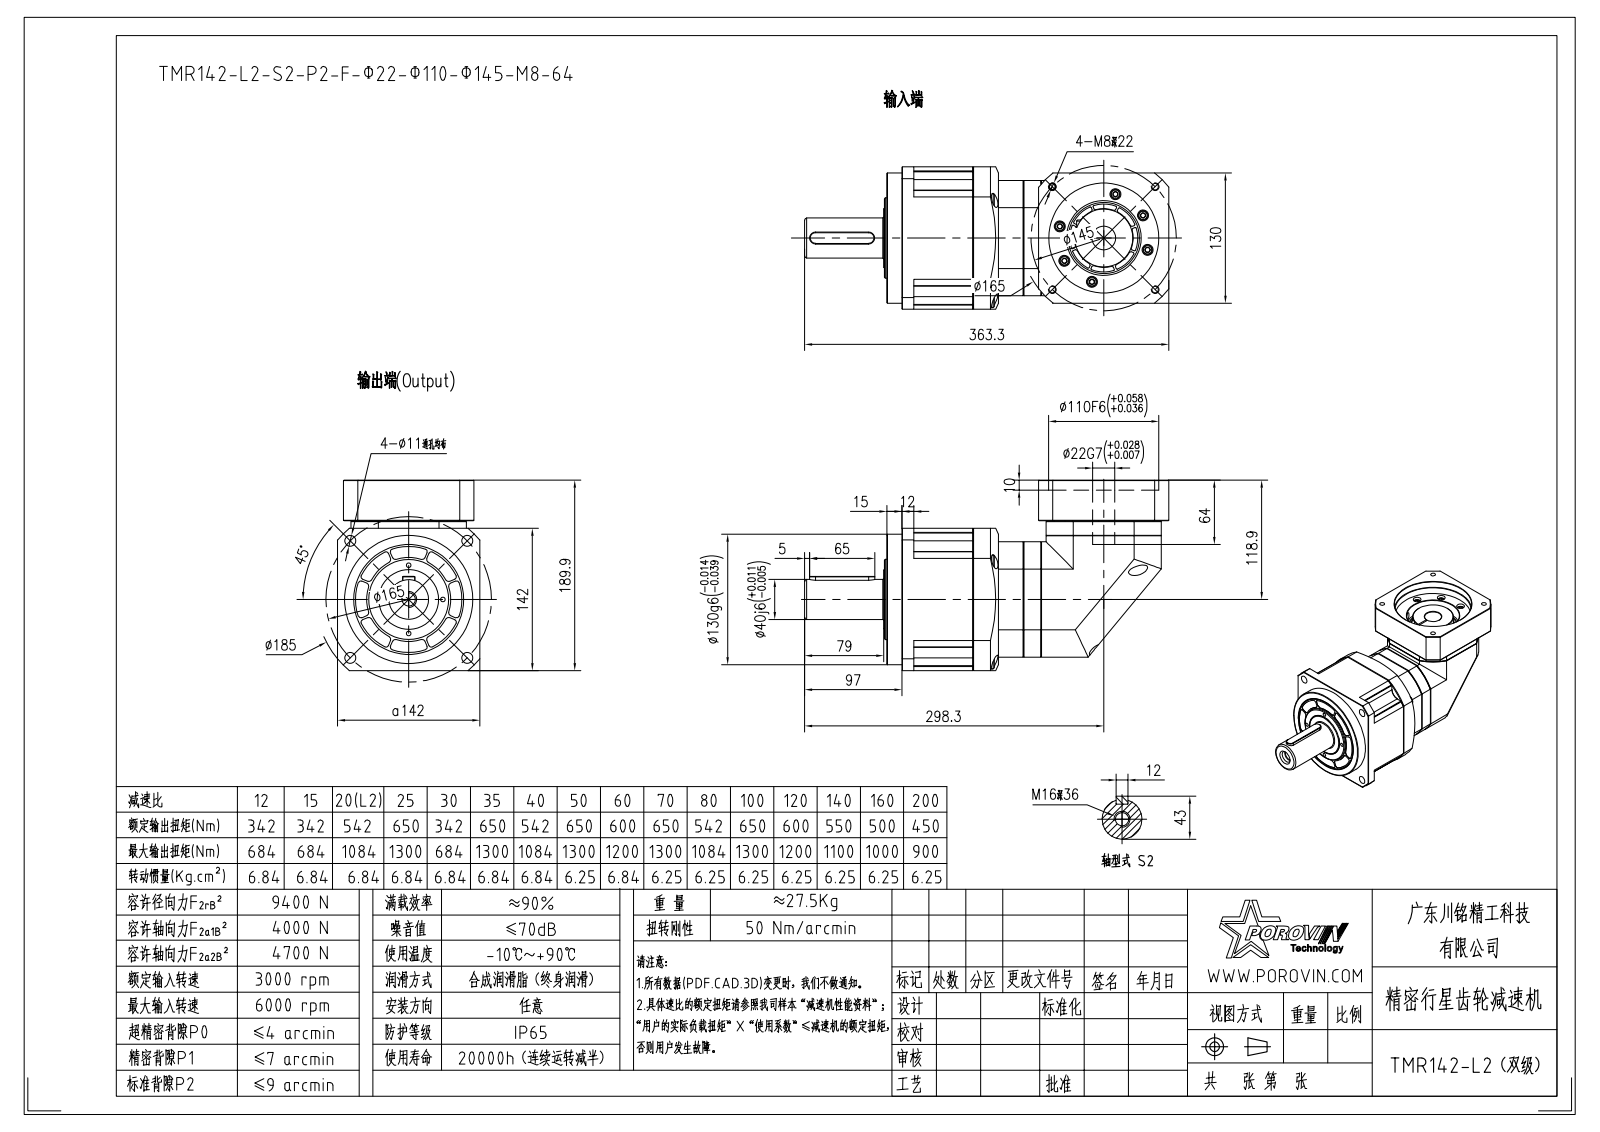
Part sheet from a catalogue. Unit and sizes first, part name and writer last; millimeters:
Units: millimetres
Overall size (bounding box): 363.3 × 189.9 × 142
Round holes (diameter × count): ⌀6.68 ×16, ⌀5 ×13, ⌀11 ×12, ⌀6.8 ×11, ⌀6.5 ×10, ⌀6.6 ×6, ⌀14 ×5, ⌀9 ×4, ⌀10.5 ×4, ⌀11.9 ×4, ⌀8.5 ×1, ⌀13.6 ×1
Round bosses / shafts (diameter × count): ⌀10 ×16, ⌀9.88 ×16, ⌀6 ×16, ⌀13 ×5, ⌀8 ×5, ⌀130 ×1, ⌀99 ×1, ⌀80 ×1
Partial cylindrical surfaces — rounded edges, fillets, slot ends (radius × count): R1 ×40, R2 ×32, R10.5 ×4, R6 ×2, R65 ×2, R5 ×1, R6.75 ×1, R42.5 ×1
Main face-to-face distances: 13.5, 128.5, 50.3, 18, 7.5, 68.3, 68.1, 17.8, 142, 115
Hole centre spacings: 45.25, 111.28, 12.31, 21.17, 47.5, 51.41, 91.96, 110.07
Volume: 4 143 000 mm³ · Surface area: 434 297 mm²
Bodies: 48 solids, 1479 faces (618 planar, 575 cylindrical, 286 other)
Part name (STEP PRODUCT): HEXAGON_SOCKET_HEAD_CAP_S-10700; SPRING_LOCK_WASHERS--NORMAL_TYP; HEXAGON_SOCKET_HEAD_CAP_S-10760; TMR1150003 (+8 more)
STEP written by: CREO PARAMETRIC BY PTC INC, 2020053 (CONFIG_CONTROL_DESIGN)
